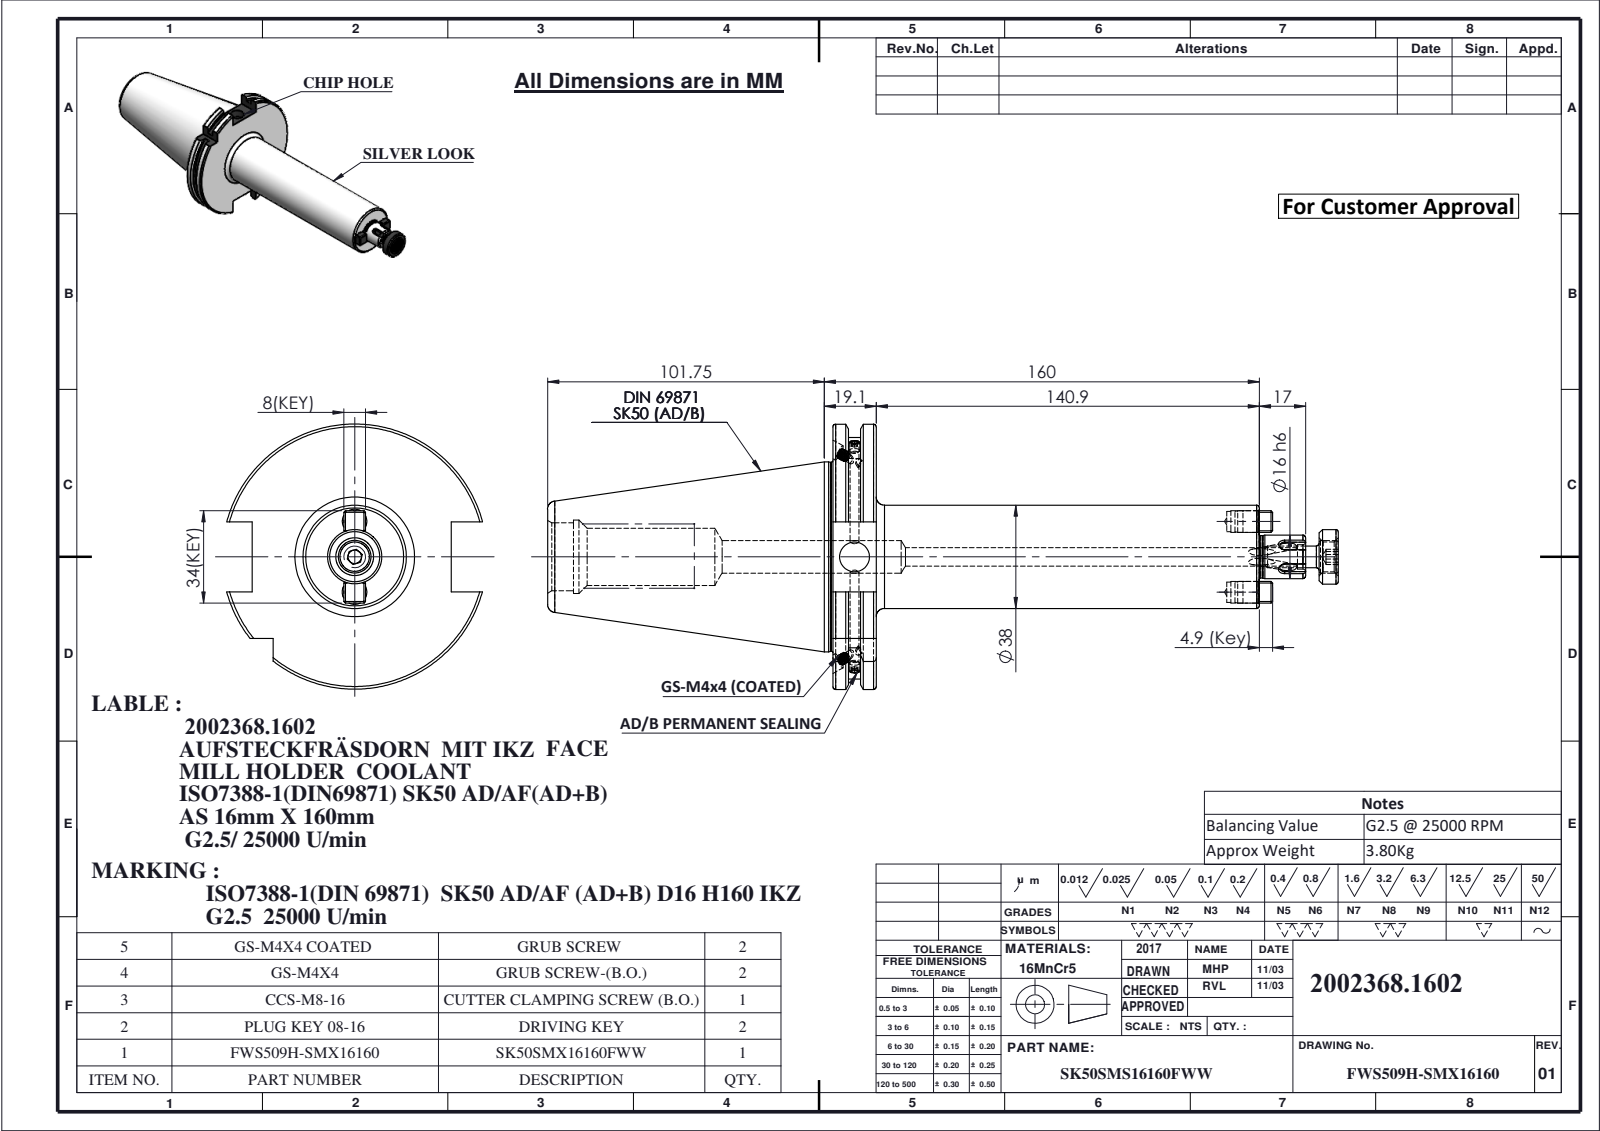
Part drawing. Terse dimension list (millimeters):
name: PLUG KEY 08-16; SK50SMX16160FWW; CCS-M8-16-2; FWS509H-SMX16160 (+4 more)
written by: SolidWorks 2024 (CONFIG_CONTROL_DESIGN)
unit: mm
bodies: 9 solids, 440 faces (130 planar, 127 cylindrical, 183 other)
size: 290.75 × 97.5 × 94.05
volume: 491 269 mm³; area: 68 908 mm²
holes: 4× ⌀3, 2× ⌀3.2, 2× ⌀6, 2× ⌀7.5, 2× ⌀8, 2× ⌀11, 1× ⌀3.3, 1× ⌀6.8, 1× ⌀9, 1× ⌀12, 1× ⌀21, 1× ⌀25
bosses: 4× ⌀4, 2× ⌀8.02, 2× ⌀7.98, 2× ⌀2.9, 1× ⌀69.85, 1× ⌀69.45, 1× ⌀38, 1× ⌀20
rounds: 4× R2, 2× R5.25, 1× R44.9, 1× R48.75
face distances: 15.9, 156.8, 140.9, 5.66, 10.24, 151.14, 10.14, 4.48, 5.76, 146.66
hole spacings: 13, 26
